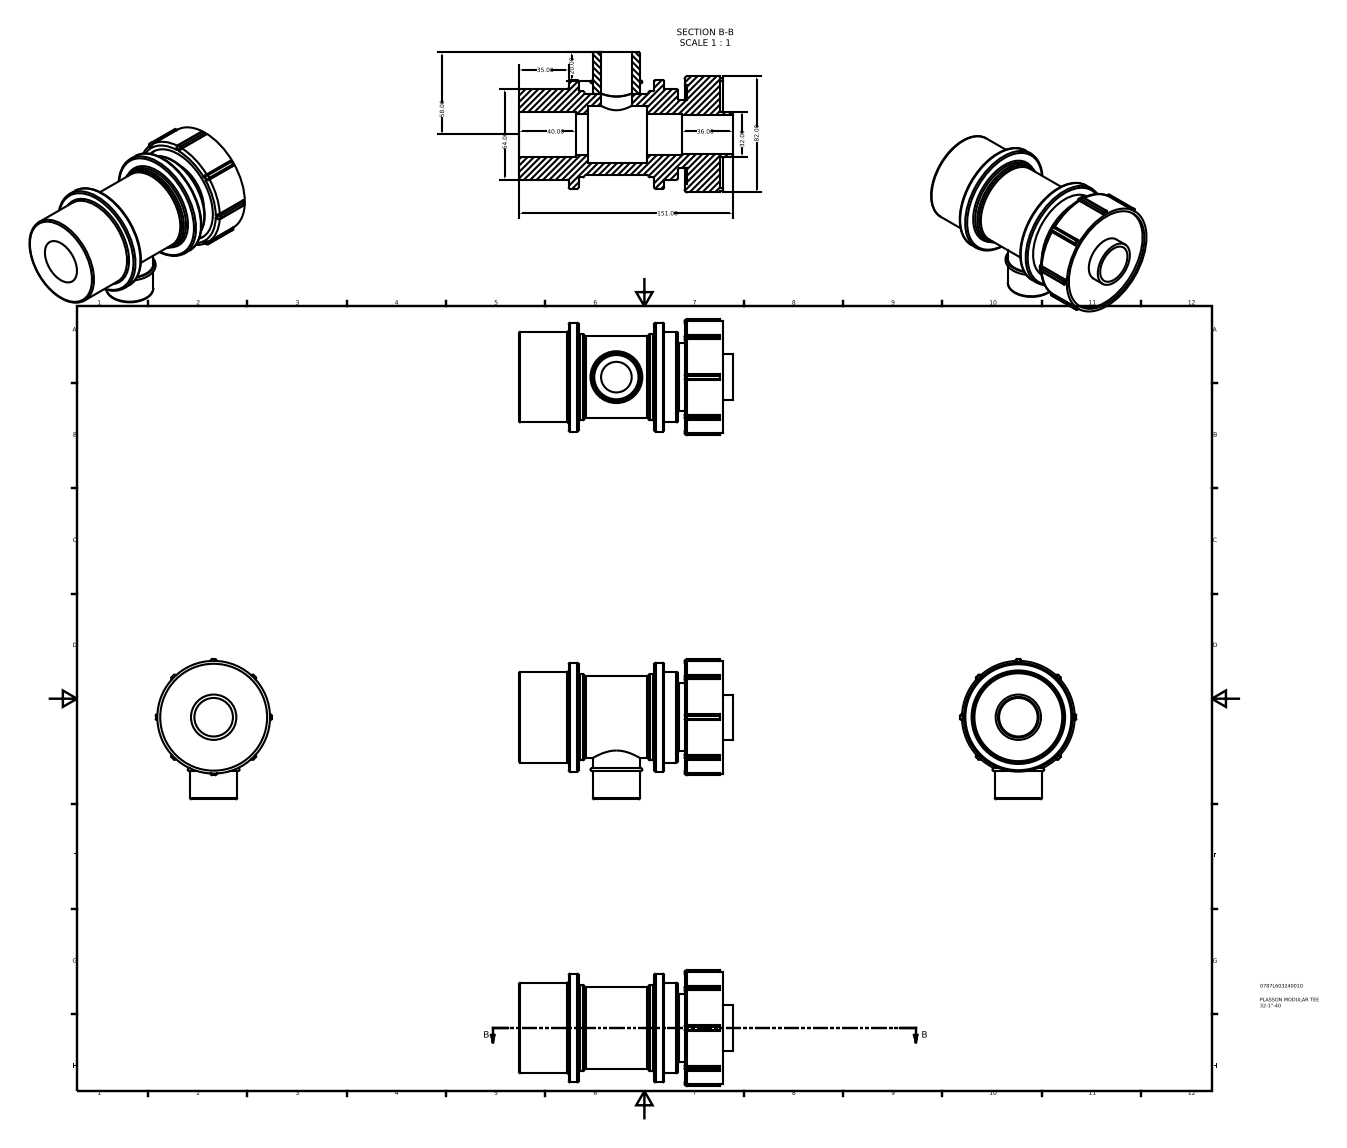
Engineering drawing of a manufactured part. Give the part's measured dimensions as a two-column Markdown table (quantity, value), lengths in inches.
| quantity | value |
| --- | --- |
| part name | 0787L603240010 |
| STEP written by | Autodesk Inventor 2015 (AUTOMOTIVE_DESIGN) |
| units | inches |
| bodies | 2 solids, 168 faces (50 planar, 62 cylindrical, 56 other) |
| overall size | 5.945 × 3.898 × 3.228 |
| volume | 22.81 in³ |
| surface area | 111.9 in² |
| round holes (diameter × count) | 0.851 × 1, 1.071 × 1, 1.134 × 1, 1.26 × 1, 1.587 × 1, 2.268 × 1, 2.744 × 1, 2.97 × 1 |
| round bosses / shafts (diameter × count) | 3.131 × 1, 3.024 × 1, 2.52 × 1, 2.394 × 1, 1.89 × 1, 1.309 × 1 |
| partial cylindrical surfaces (radius × count) | 0.039 × 28, 0.079 × 8 |
| main face-to-face distances | 5.591, 0.276, 2.378, 4.669, 0.921, 1.654, 3.016, 3.937, 3.756, 2.102 |
